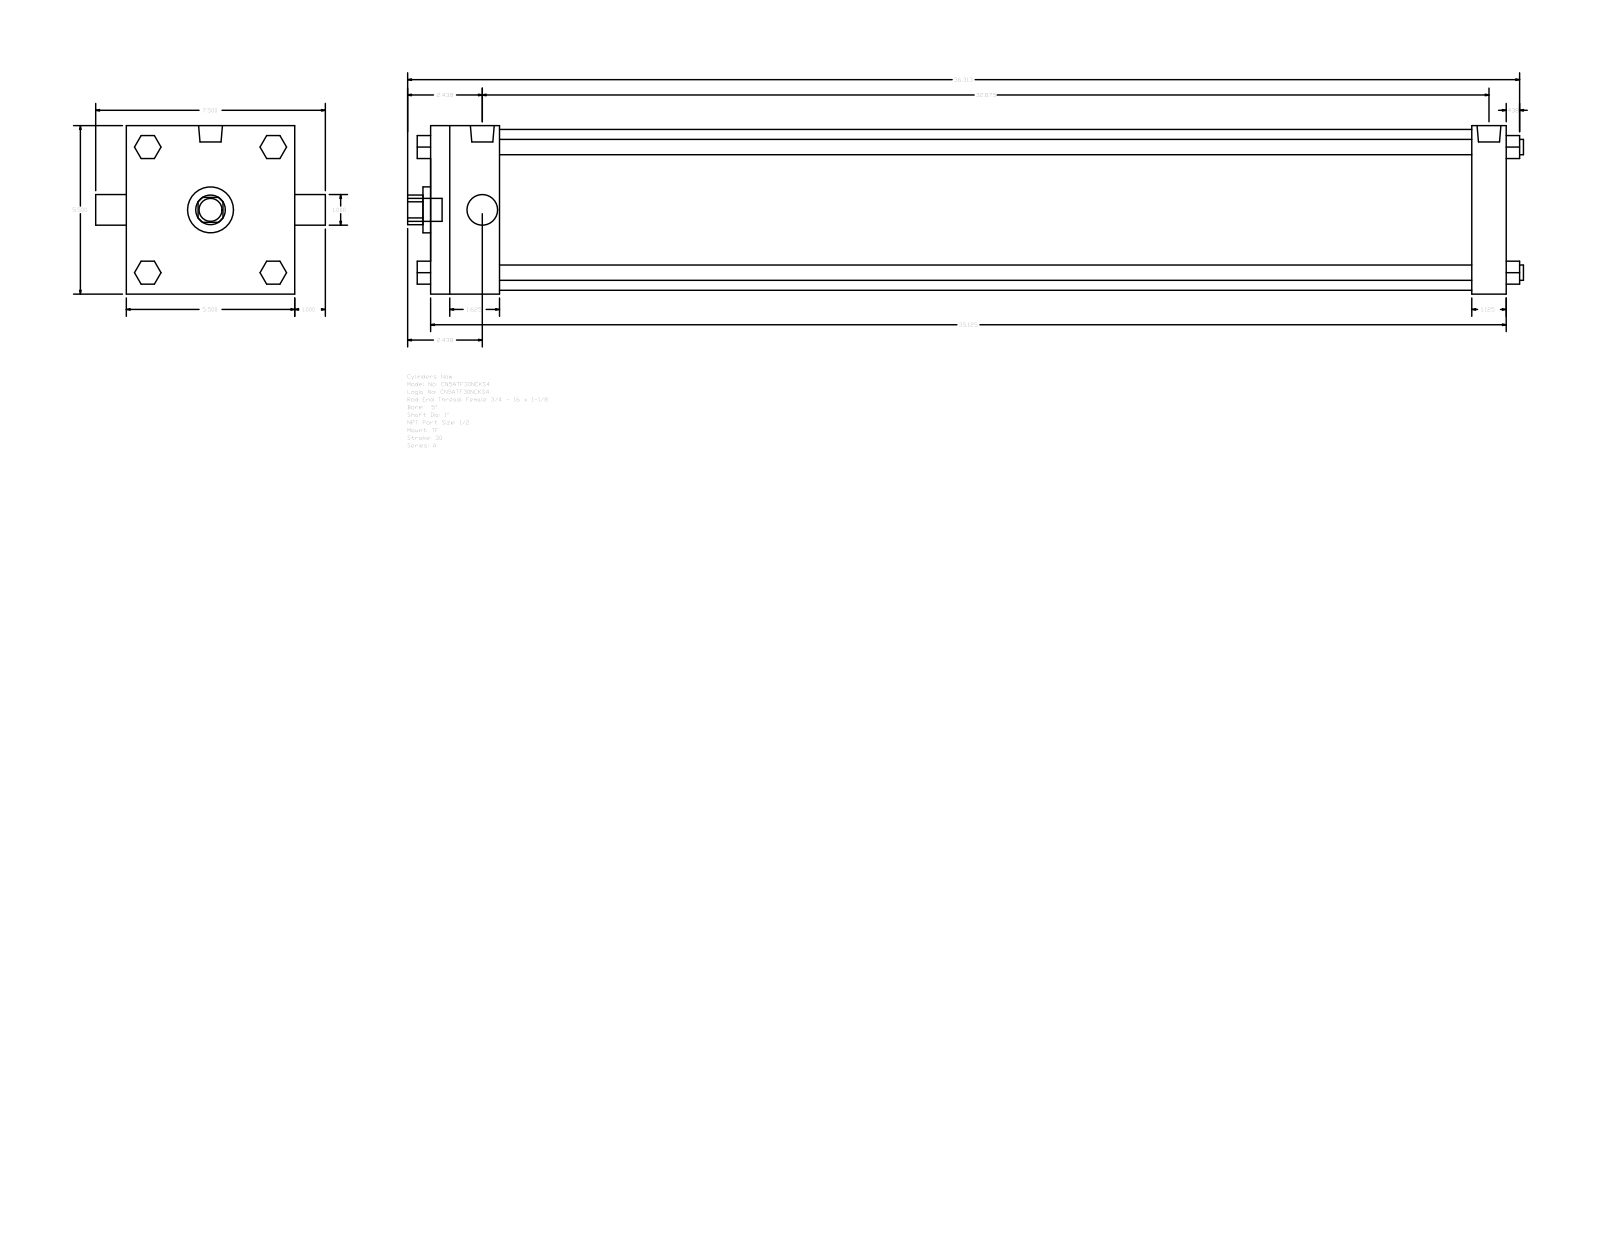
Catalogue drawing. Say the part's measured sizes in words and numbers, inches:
The part is named "A_TF__0500_1". Its 3-D file was written by "GSSL Pune (CONFIG_CONTROL_DESIGN)". It is 0 solids with 120 faces: 92 planar, 28 cylindrical and 0 other. Overall it measures 36.437 by 7.5 by 5.5 inches. Round holes: 2 of diameter 1, 1 of diameter 1.5, 1 of diameter 5.25. Round bosses or shafts: 4 of diameter 0.5, 3 of diameter 0.344, 2 of diameter 0.778, 1 of diameter 0.75. Partial cylindrical surfaces (rounded edges, fillets, slot ends): 1 of radius 0.484. The main face-to-face distances are 5.5, 35.125, 34, 1.125, 2.25, 31.75, 32.875, 0.75, 2.05, 3.55.
